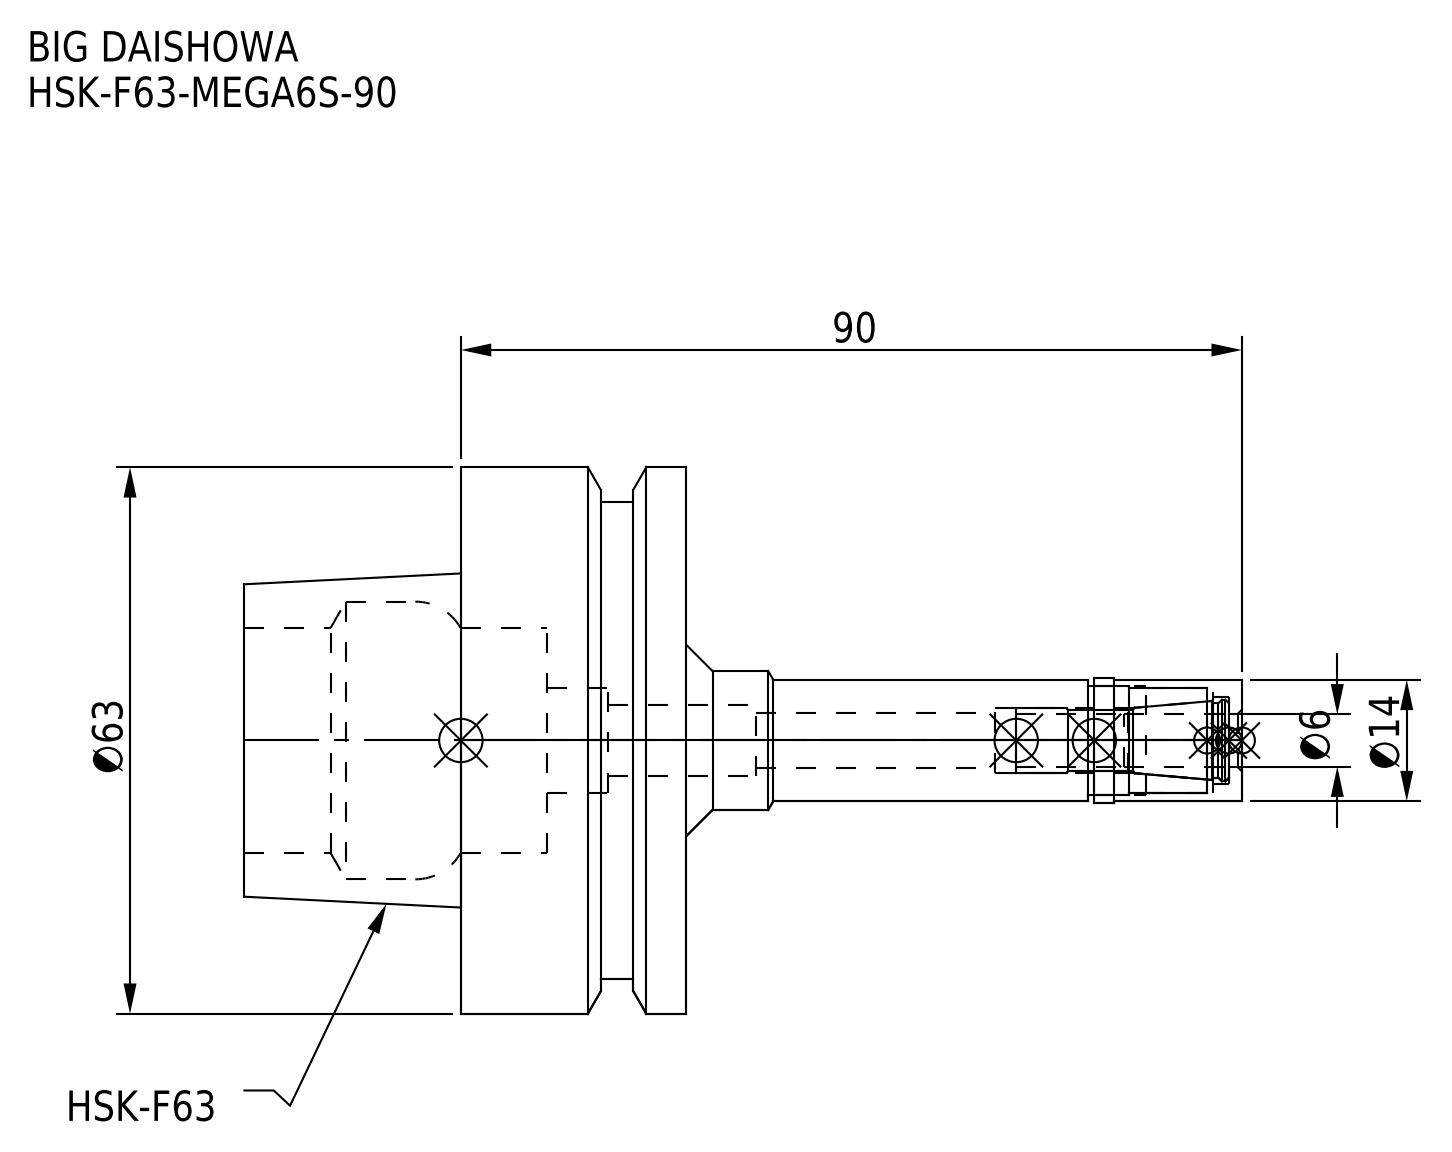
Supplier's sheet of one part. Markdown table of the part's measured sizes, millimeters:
| quantity | value |
| --- | --- |
| part name | DXF_TEMP_ASSY_ASM_4_ASM.stp; HSK-F63-MEGA6S-90_1.stp; MGN6S_1.stp; HSK-F63-MEGA6S-90-060-FreeParts (+3 more) |
| STEP written by | SolidWorks 2019 (CONFIG_CONTROL_DESIGN) |
| units | millimeters |
| bodies | 2 solids, 78 faces (18 planar, 42 cylindrical, 18 other) |
| overall size | 115 × 63 × 63 |
| volume | 89 345 mm³ |
| surface area | 24 367 mm² |
| round holes (diameter × count) | 6.1 × 1, 6.4 × 1, 7.4 × 1, 8.25 × 1, 10 × 1, 12 × 1, 12.5 × 1, 26 × 1, 32 × 1 |
| round bosses / shafts (diameter × count) | 63 × 1, 55 × 1, 16 × 1, 14.3 × 1, 14 × 1 |
| main face-to-face distances | 26, 51, 25, 16.05, 9.95, 34.95, 6.12, 9.93, 19.88, 44.88 |
